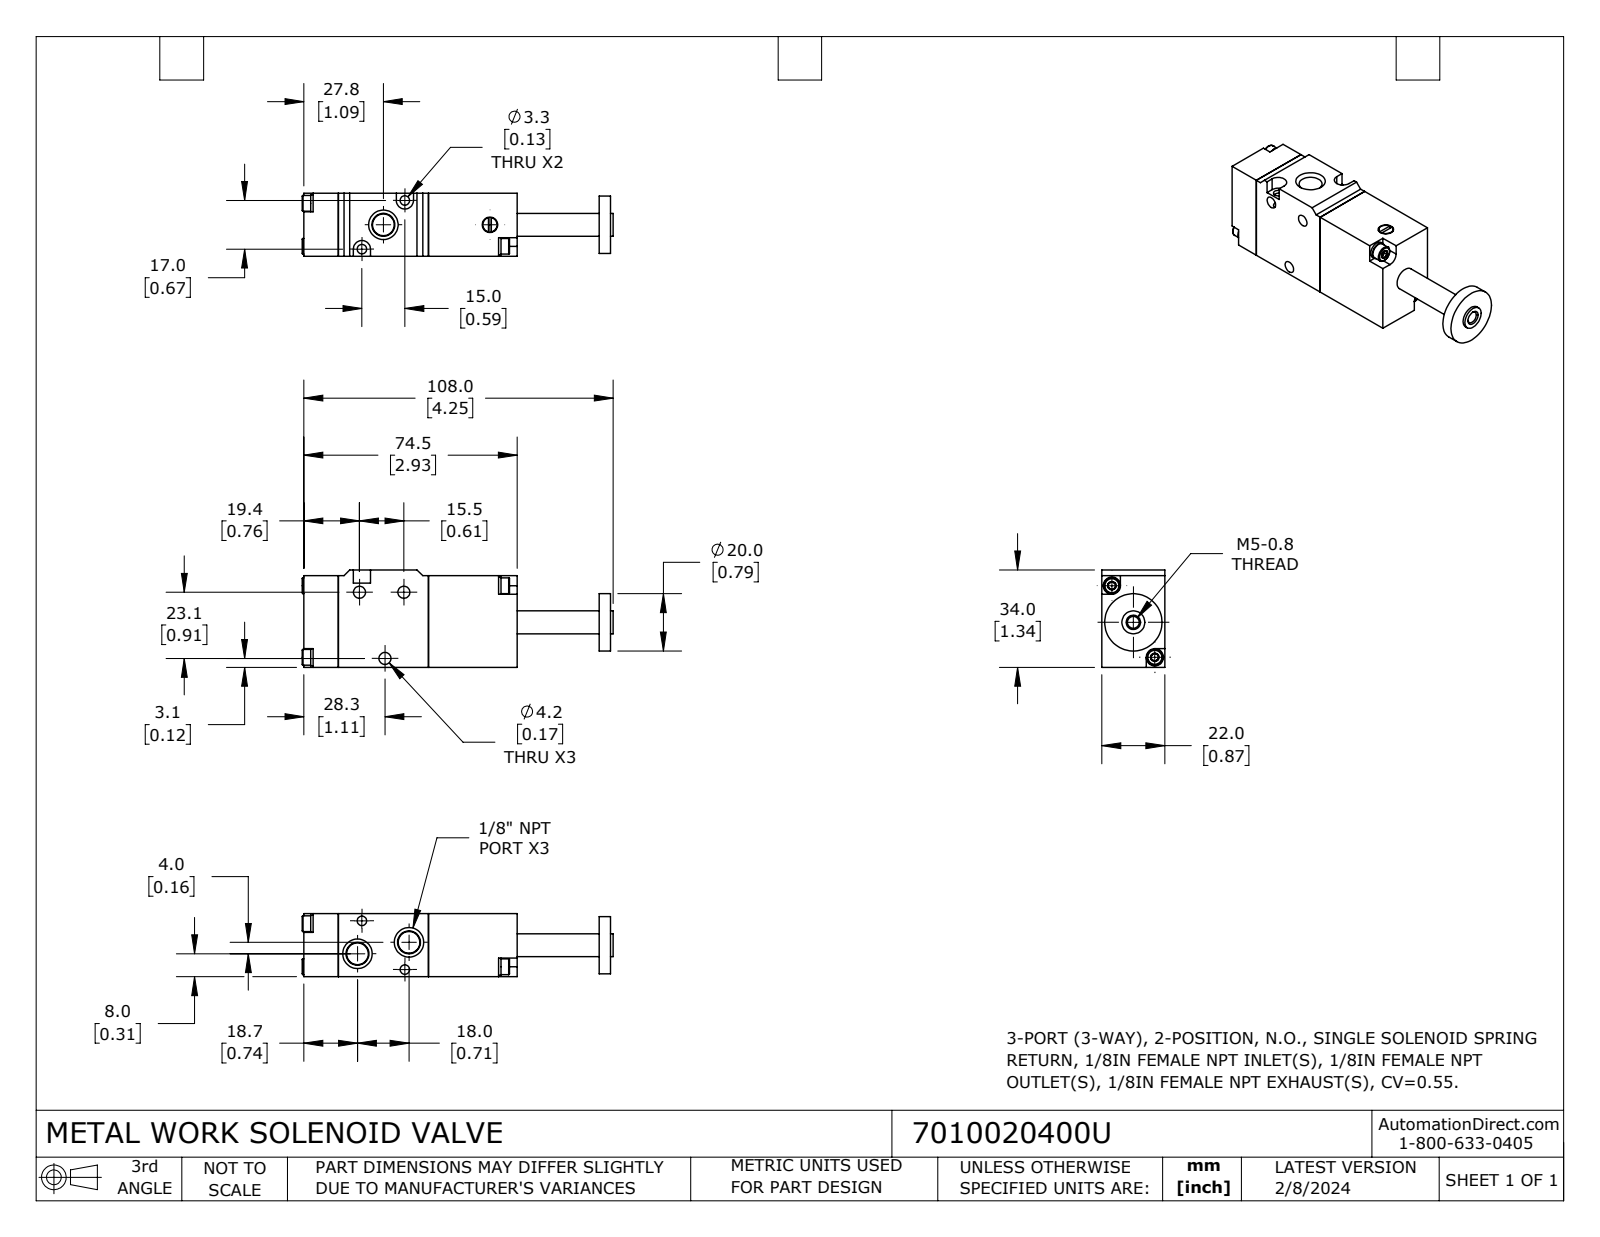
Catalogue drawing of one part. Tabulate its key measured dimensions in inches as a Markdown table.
| quantity | value |
| --- | --- |
| part name | 7010020400U |
| STEP written by | SolidWorks 2023 (CONFIG_CONTROL_DESIGN) |
| units | inches |
| bodies | 11 solids, 254 faces (120 planar, 64 cylindrical, 70 other) |
| overall size | 4.276 × 1.339 × 0.866 |
| volume | 3.251 in³ |
| surface area | 26.36 in² |
| round holes (diameter × count) | 0.118 × 4, 0.165 × 3, 0.13 × 2, 0.163 × 1, 0.213 × 1 |
| round bosses / shafts (diameter × count) | 0.236 × 4, 0.217 × 4, 0.787 × 1, 0.315 × 1, 0.197 × 1 |
| partial cylindrical surfaces (radius × count) | 0.118 × 2 |
| main face-to-face distances | 0.866, 1.24, 1.26, 0.472, 1.713, 1.22, 2.933, 2.461, 1.339, 0.079 |
| hole center spacings | 0.564, 0.584, 0.591, 0.984, 1.148, 0.61, 0.893, 0.946 |
